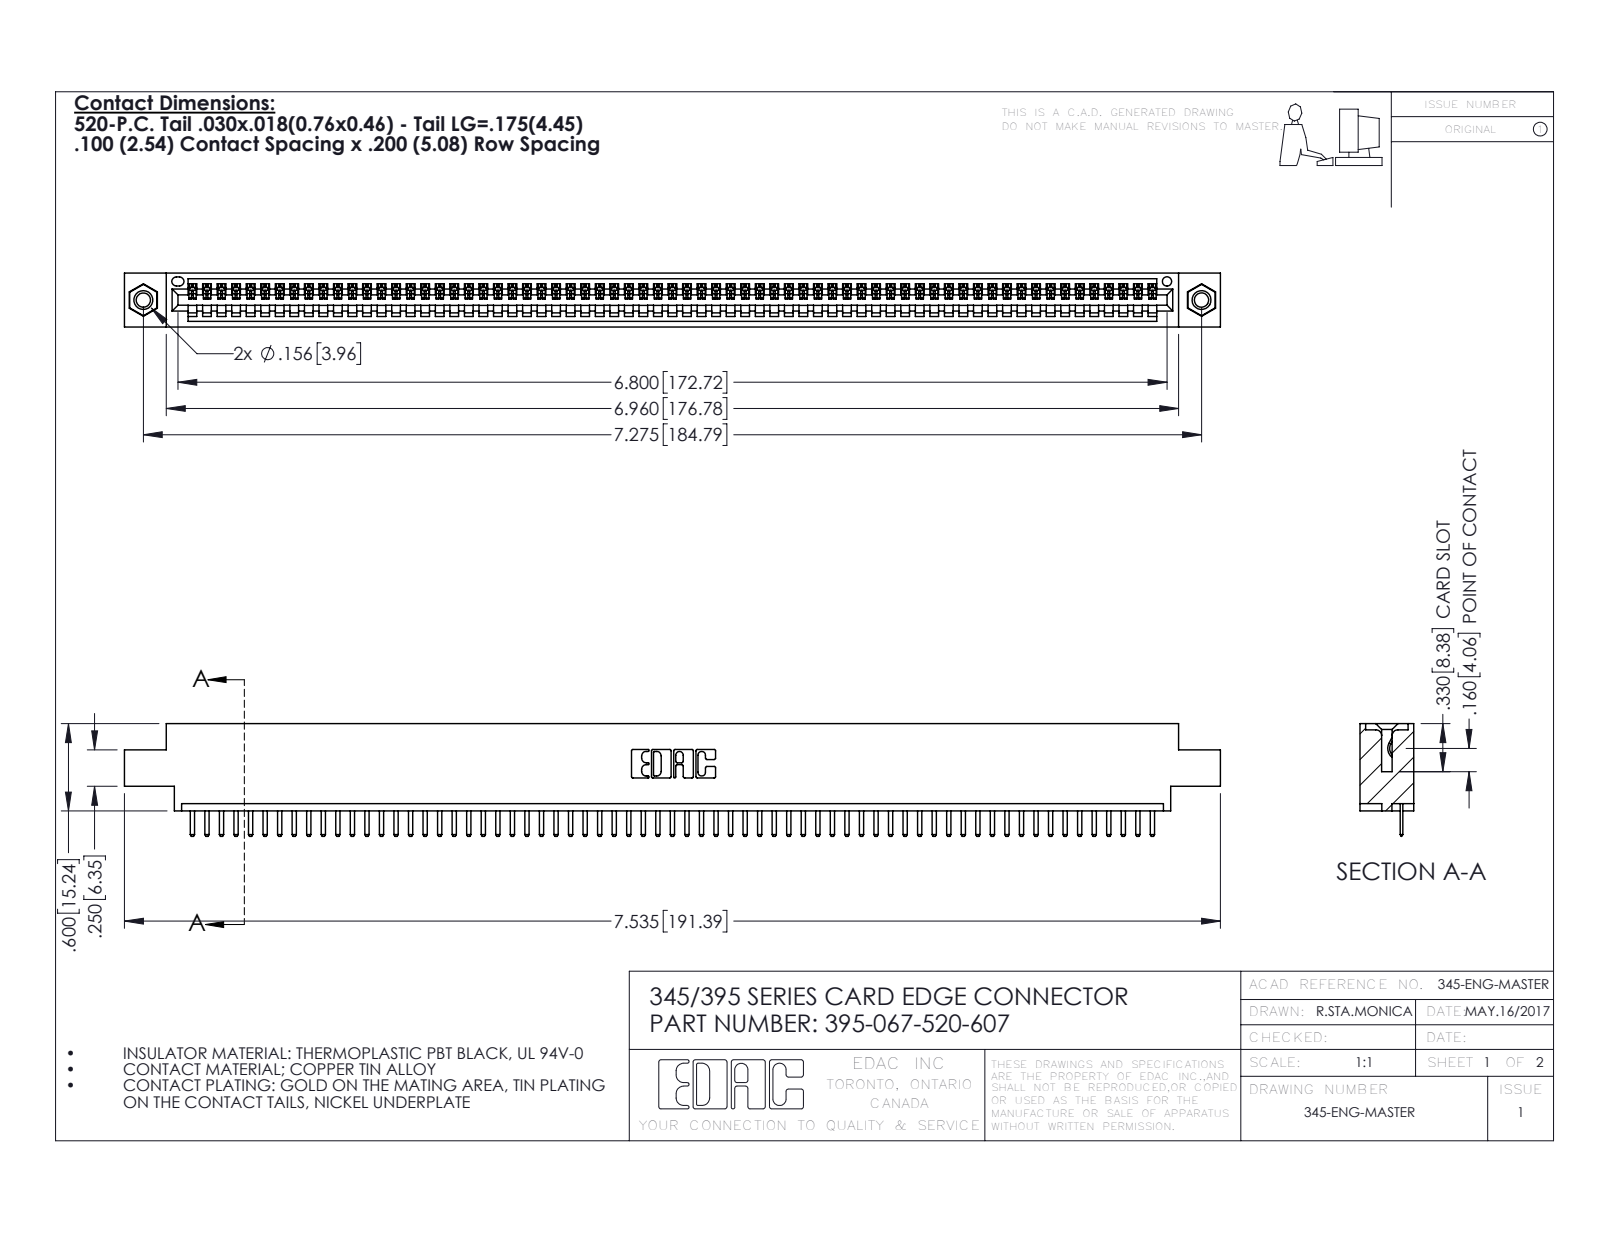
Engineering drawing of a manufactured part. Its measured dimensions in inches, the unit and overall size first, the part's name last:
Units: inches
Overall size (bounding box): 7.535 × 0.775 × 0.37
Round holes (diameter × count): ⌀0.098 ×2, ⌀0.125 ×2, ⌀0.156 ×2, ⌀0.064 ×1
Round bosses / shafts (diameter × count): ⌀0.155 ×2
Partial cylindrical surfaces — rounded edges, fillets, slot ends (radius × count): R0.01 ×136, R0.006 ×134, R0.01 ×22, R0.007 ×6, R0.031 ×6, R0.026 ×3, R0.031 ×2, R0.04 ×2
Main face-to-face distances: 0.072, 0.298, 0.37, 0.2, 0.098, 0.272, 0.025, 0.225, 0.072, 0.175
Hole centre spacings: 0.27, 7.039, 7.275
Volume: 1.102 in³ · Surface area: 37 in²
Bodies: 70 solids, 4344 faces (2930 planar, 1398 cylindrical, 16 other)
Part name (STEP PRODUCT): 395-067-520-607; 345-292-001_345-293-120; 345 Part_0.170 Offset - 0.156 Dia-TI; 345-250-001_345-250-005-103
STEP written by: SolidWorks 2016 (CONFIG_CONTROL_DESIGN)
